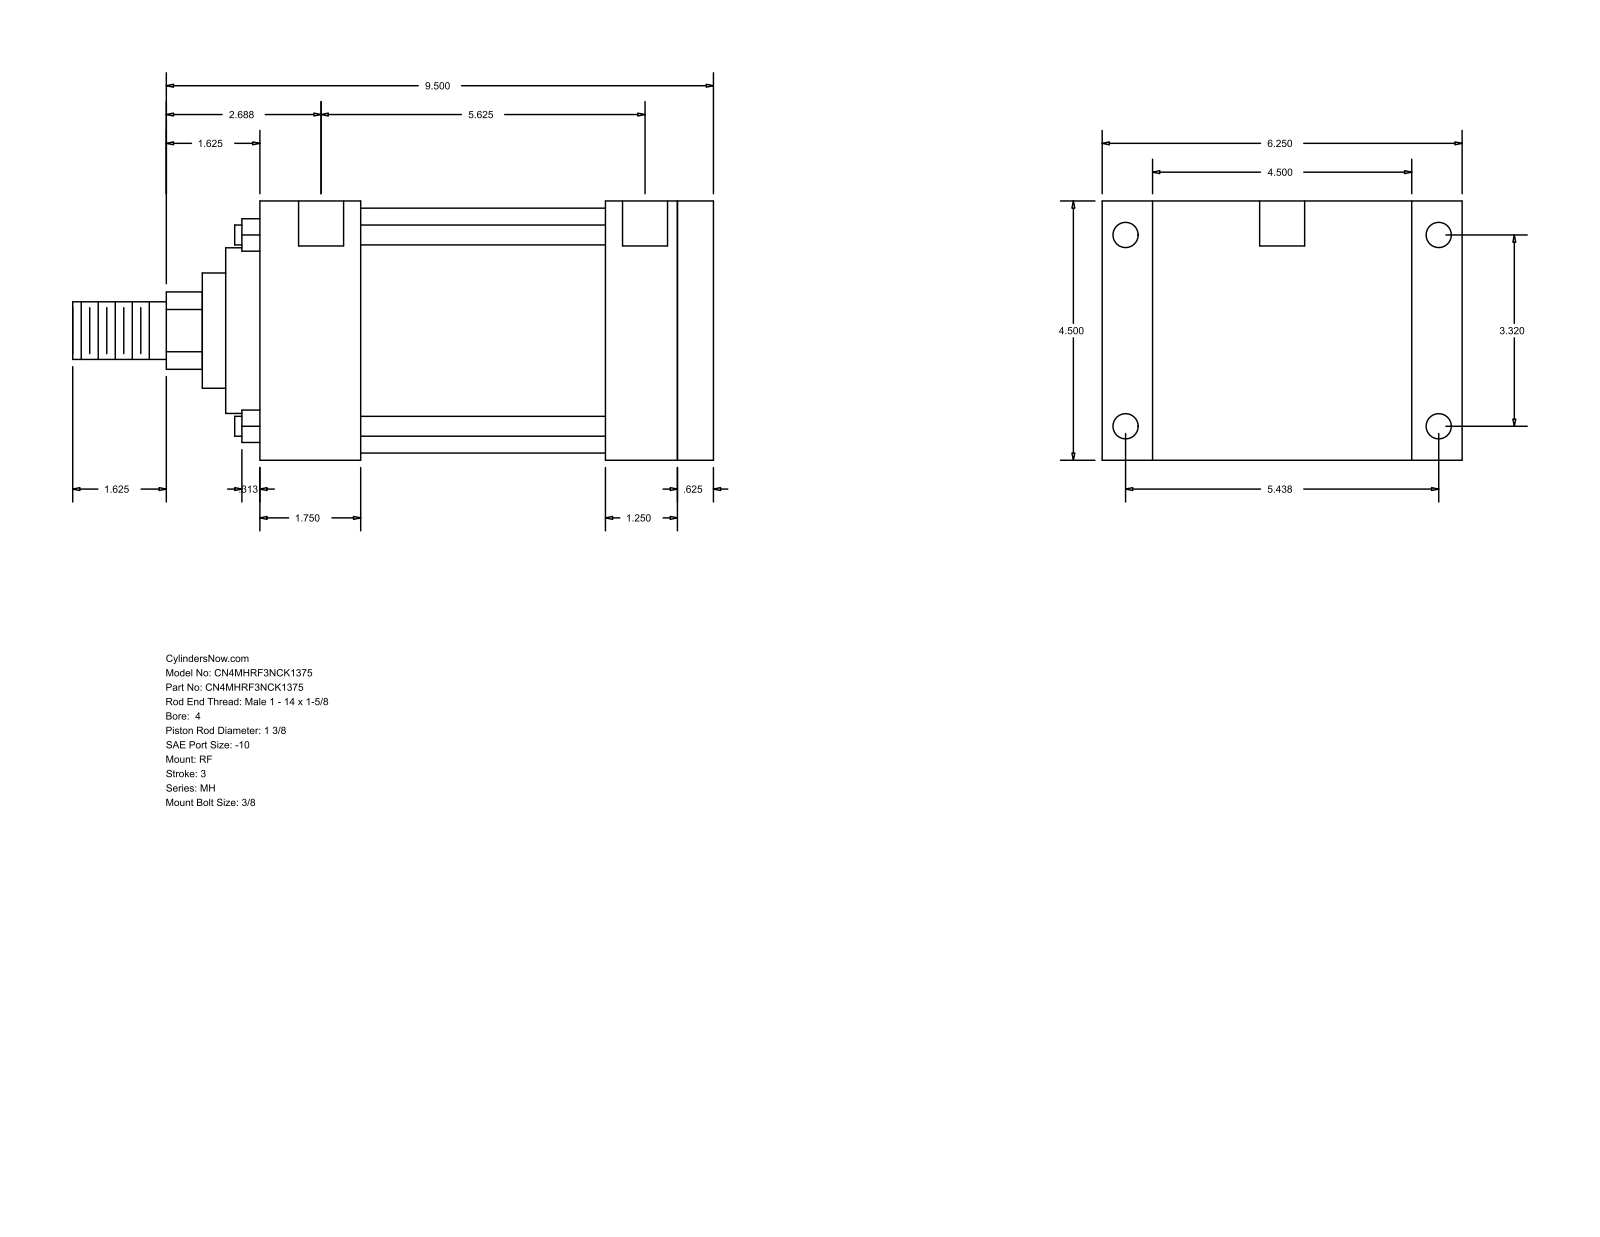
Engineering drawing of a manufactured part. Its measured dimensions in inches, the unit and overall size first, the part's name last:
Units: inches
Overall size (bounding box): 11.125 × 6.25 × 4.5
Round holes (diameter × count): ⌀0.344 ×4, ⌀0.438 ×4, ⌀0.781 ×2
Round bosses / shafts (diameter × count): ⌀0.345 ×4, ⌀4.25 ×1, ⌀2.875 ×1, ⌀2 ×1, ⌀1.375 ×1, ⌀1 ×1
Partial cylindrical surfaces — rounded edges, fillets, slot ends (radius × count): R0.672 ×1
Main face-to-face distances: 4.5, 7.875, 7.25, 0.625, 1.75, 5.5, 6.125, 6, 4.25, 1.25
Hole centre spacings: 3.32, 5.438, 5.75, 6.371, 0.062, 0.063, 5.625, 5.687
Bodies: 0 solids, 94 faces (65 planar, 29 cylindrical, 0 other)
Part name (STEP PRODUCT): MH_RF__0400_1.375
STEP written by: GSSL Pune (CONFIG_CONTROL_DESIGN)
